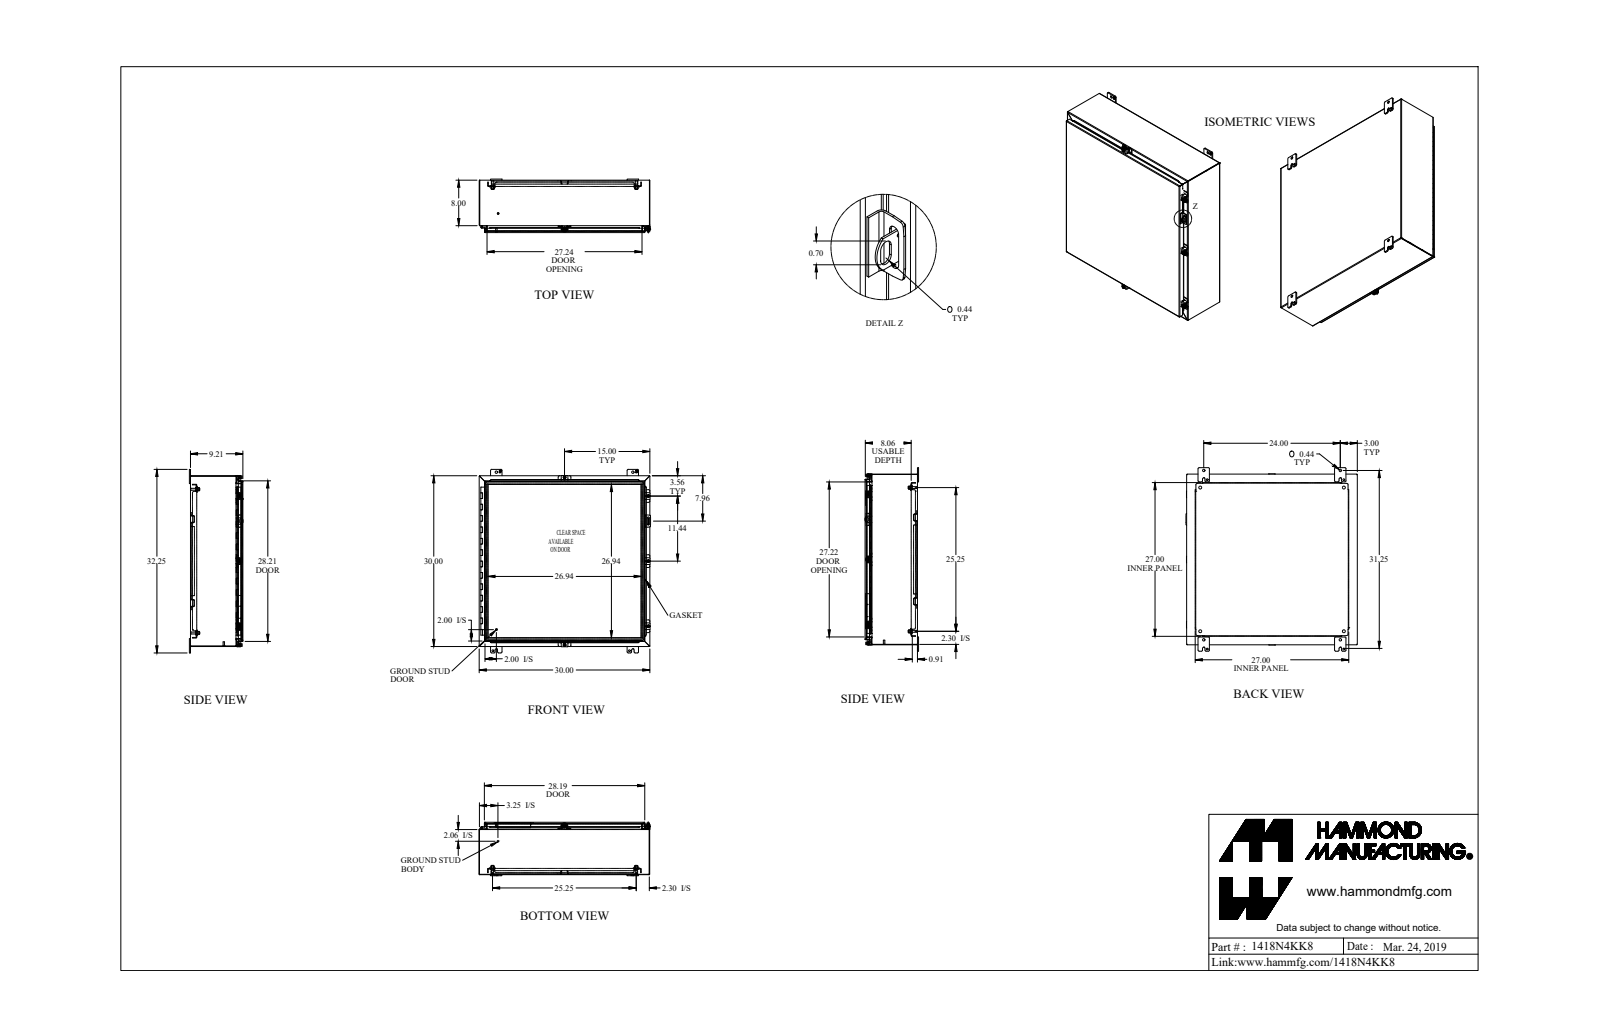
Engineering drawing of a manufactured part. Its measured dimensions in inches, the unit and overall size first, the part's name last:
Units: inches
Overall size (bounding box): 32.25 × 30.126 × 9.437
Round holes (diameter × count): ⌀0.213 ×5, ⌀0.265 ×5, ⌀0.375 ×5, ⌀0.313 ×4, ⌀0.437 ×4, ⌀0.5 ×4, ⌀0.307 ×2, ⌀0.445 ×2, ⌀0.125 ×1, ⌀0.187 ×1
Round bosses / shafts (diameter × count): ⌀0.5 ×5, ⌀0.39 ×5, ⌀0.244 ×5, ⌀0.65 ×4, ⌀0.375 ×4, ⌀0.33 ×4, ⌀1 ×2, ⌀0.281 ×2
Partial cylindrical surfaces — rounded edges, fillets, slot ends (radius × count): R0.188 ×32, R0.25 ×32, R0.048 ×27, R0.143 ×27, R0.036 ×24, R0.108 ×24, R0.116 ×12, R0.125 ×12
Main face-to-face distances: 0.072, 0.072, 29.928, 9.066, 9.138, 9.138, 9.21, 0.095, 8.106, 8.034
Hole centre spacings: 12.803, 25.25, 30.146, 35.709, 30.146, 24, 38.224, 1.736
Volume: 327.8 in³ · Surface area: 8 566 in²
Bodies: 46 solids, 1703 faces (1027 planar, 590 cylindrical, 86 other)
Part name (STEP PRODUCT): 1418N4KK8_Default
STEP written by: SolidWorks 2019 (CONFIG_CONTROL_DESIGN)
